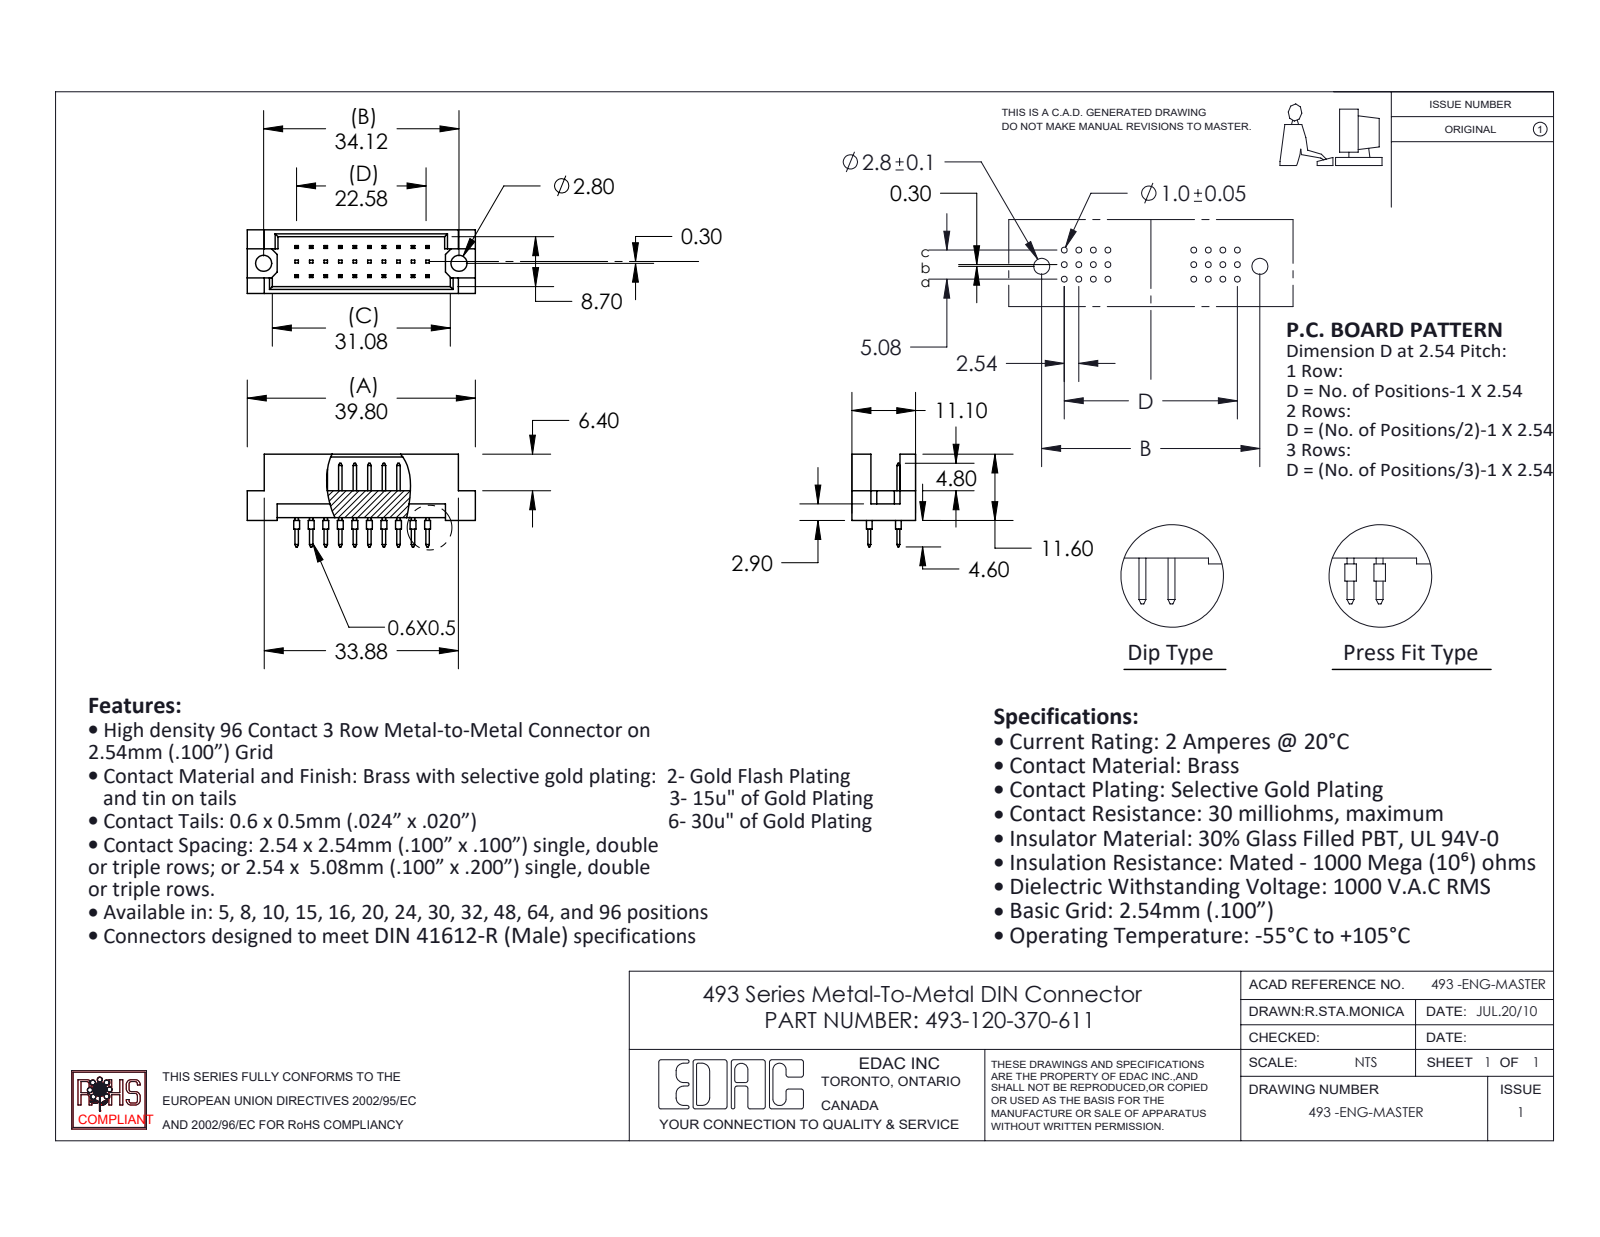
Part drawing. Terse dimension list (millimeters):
name: 493-120-370-611; 493 Part_30; 493-290_70
written by: SolidWorks 2020 (CONFIG_CONTROL_DESIGN)
unit: mm
bodies: 21 solids, 612 faces (568 planar, 44 cylindrical, 0 other)
size: 39.8 × 16.2 × 11.1
volume: 2 473 mm³; area: 3 420 mm²
holes: 2× ⌀2.8
bosses: 20× ⌀1
face distances: 1.2, 9.9, 5.08, 11.1, 2.54, 0.5, 8.7, 4.7, 2.76, 3.26
hole spacings: 34.12
